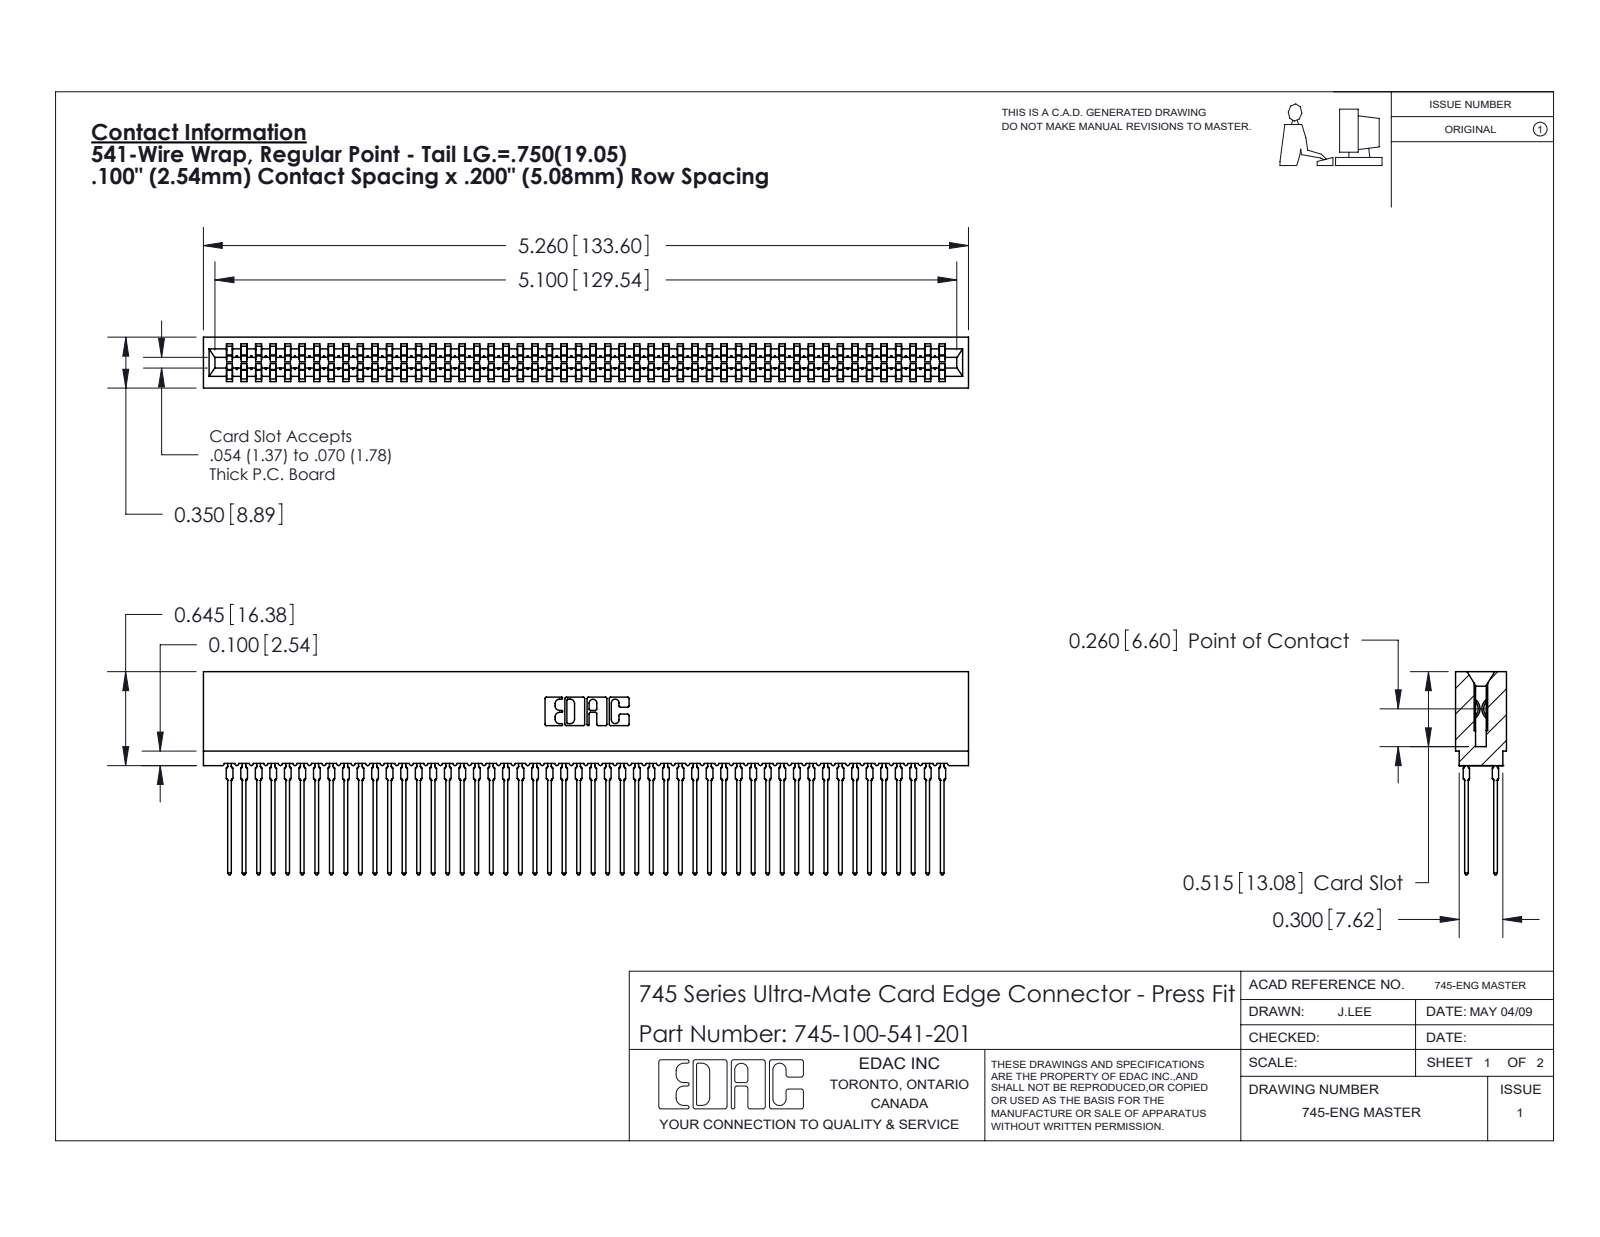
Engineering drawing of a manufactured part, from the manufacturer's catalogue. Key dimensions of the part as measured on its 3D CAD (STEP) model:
Part name (STEP PRODUCT): 745-100-541-201; 745-292-001_541; 745 Part_Insulator Option - 01
STEP written by: SolidWorks 2020 (CONFIG_CONTROL_DESIGN)
Units: inches
Bodies: 101 solids, 9045 faces (4655 planar, 1790 cylindrical, 2600 other)
Overall size (bounding box): 5.26 × 1.396 × 0.35
Volume: 0.761 in³ · Surface area: 42.67 in²
Partial cylindrical surfaces — rounded edges, fillets, slot ends (radius × count): R0.021 ×200, R0.015 ×100, R0.01 ×22, R0.005 ×8, R0.011 ×8, R0.007 ×6, R0.031 ×6, R0.026 ×3
Main face-to-face distances: 0.063, 0.287, 0.2, 0.35, 0.087, 0.263, 0.025, 0.045, 0.305, 0.018
